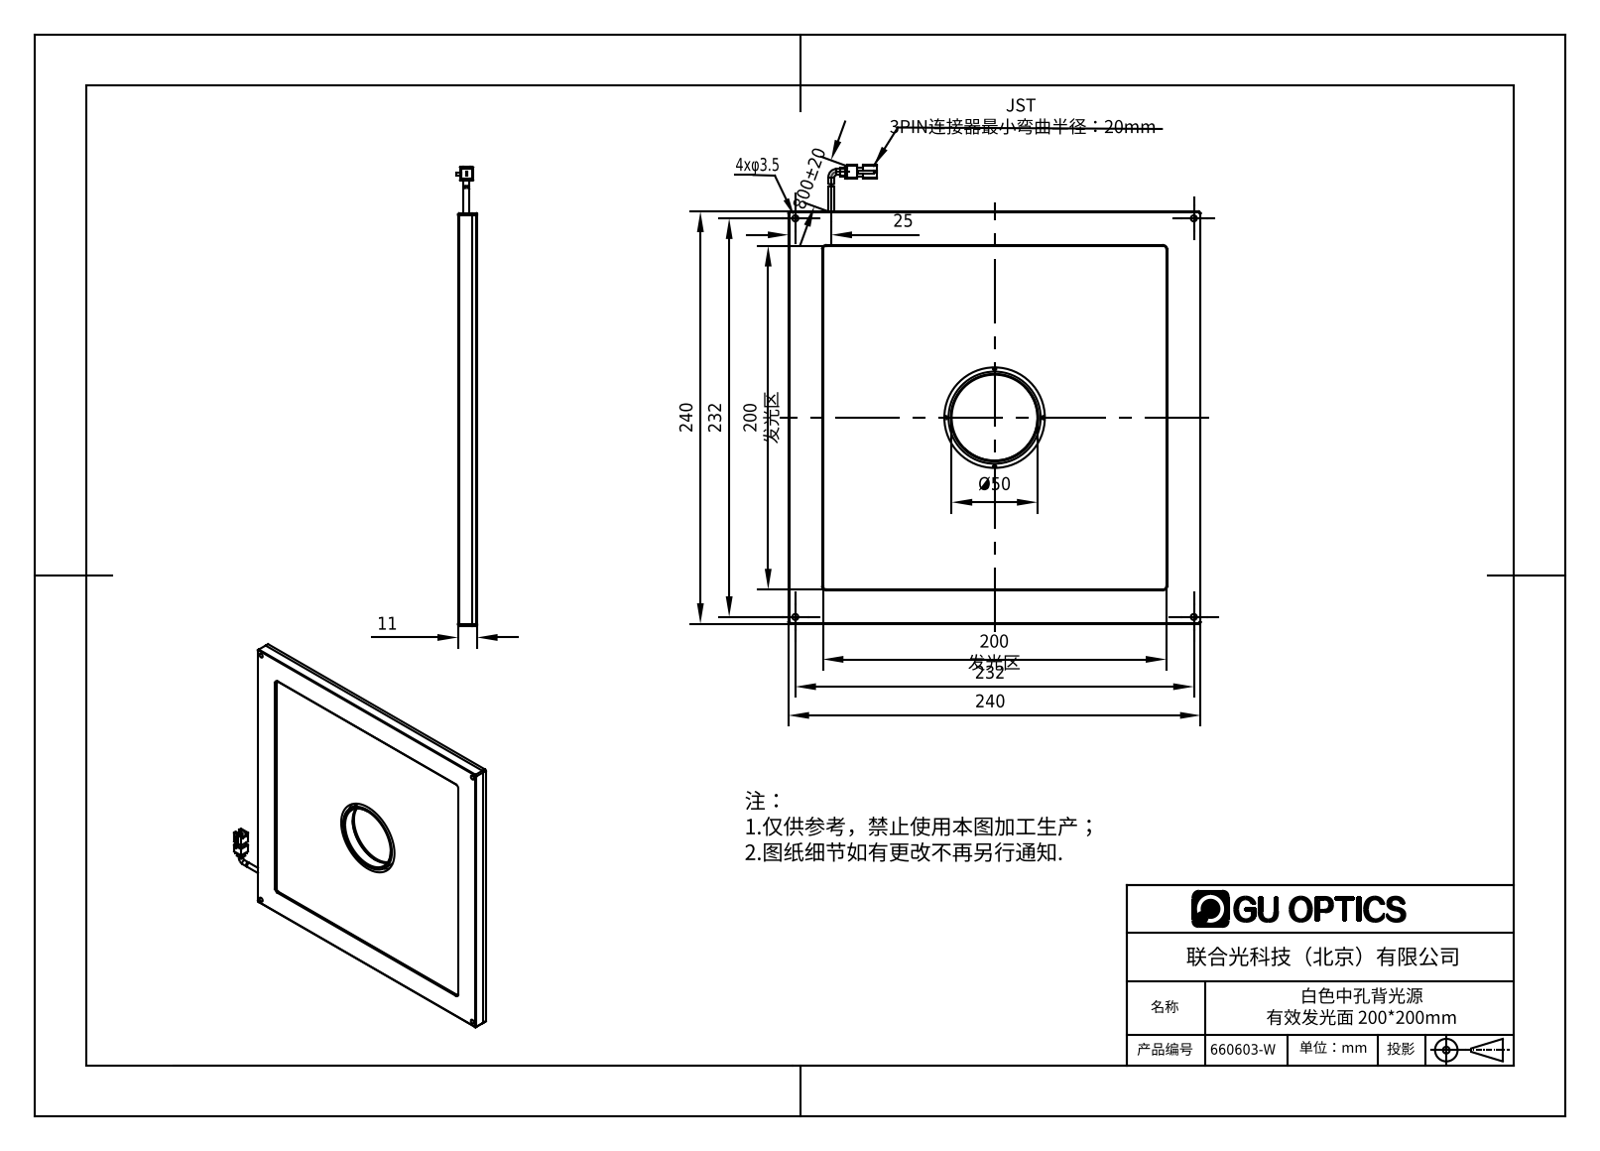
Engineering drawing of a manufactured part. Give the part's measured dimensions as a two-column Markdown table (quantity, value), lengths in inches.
| quantity | value |
| --- | --- |
| part name | 660603-W |
| STEP written by | SolidWorks 2016 (AUTOMOTIVE_DESIGN) |
| units | inches |
| bodies | 6 solids, 509 faces (192 planar, 170 cylindrical, 147 other) |
| overall size | 10.512 × 9.449 × 0.472 |
| volume | 33.63 in³ |
| surface area | 425.6 in² |
| round holes (diameter × count) | 0.079 × 20, 0.063 × 16, 0.094 × 16, 0.138 × 4, 1.969 × 1, 2.303 × 1, 2.441 × 1 |
| round bosses / shafts (diameter × count) | 0.138 × 2, 2.11 × 1 |
| partial cylindrical surfaces (radius × count) | 0.02 × 8, 0.039 × 6, 0.059 × 4, 0.079 × 4, 0.197 × 4 |
| main face-to-face distances | 0.118, 0.386, 0.268, 0.315, 0.047, 0.433, 0.039, 0.394, 0.276, 0.236 |
| hole center spacings | 0.243, 2.874, 3.111, 3.183, 4.85, 5.787, 6.024, 6.09 |
